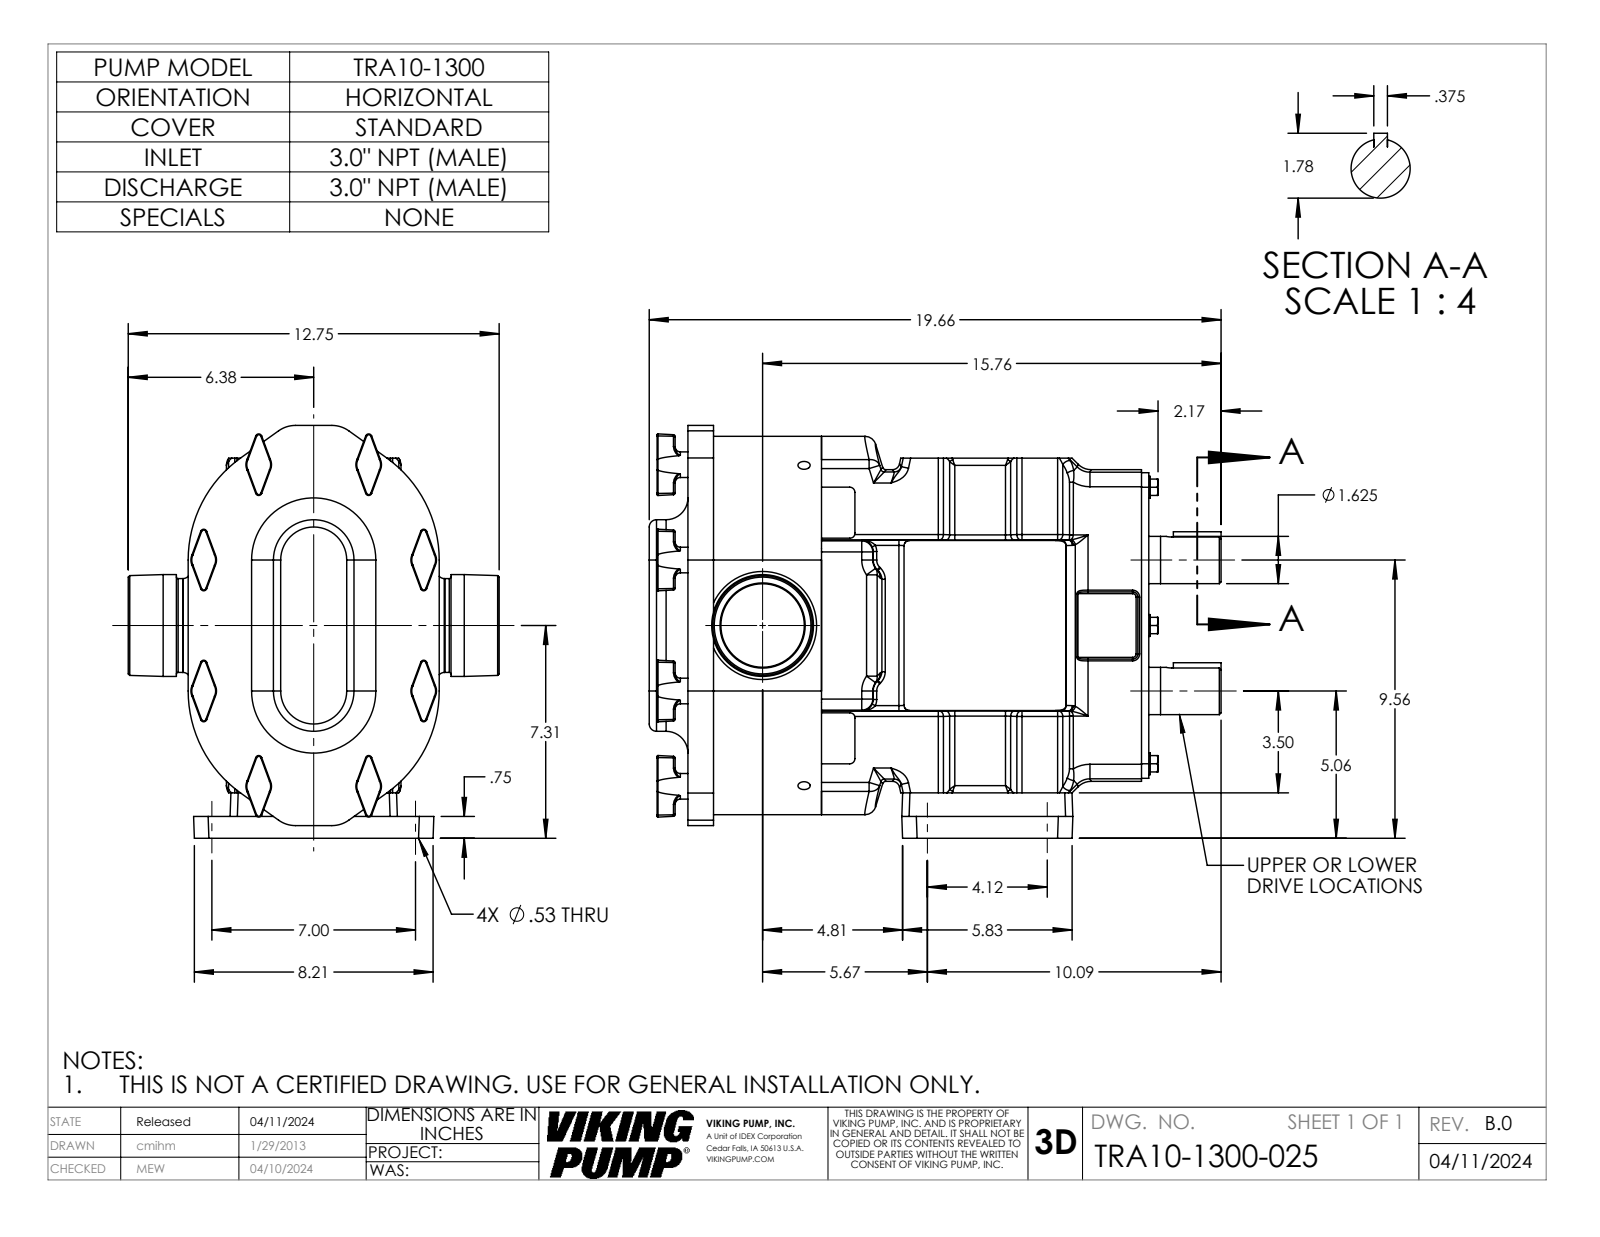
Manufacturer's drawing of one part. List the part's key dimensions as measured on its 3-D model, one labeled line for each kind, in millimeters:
Part name (STEP PRODUCT): TRA10-1300-025; TRA10-0600-COVER-STD; 1300NPT30; TRA10-0600-GEARBOX-H (+1 more)
STEP written by: SolidWorks 2022 (AUTOMOTIVE_DESIGN)
Units: millimetres
Bodies: 5 solids, 1071 faces (287 planar, 380 cylindrical, 404 other)
Overall size (bounding box): 499.3 × 360.3 × 323.9
Volume: 21 010 000 mm³ · Surface area: 916 800 mm²
Round holes (diameter × count): ⌀8.4 ×4, ⌀13.5 ×4, ⌀72.8 ×1
Round bosses / shafts (diameter × count): ⌀22.4 ×8, ⌀19.1 ×6, ⌀41.2 ×2, ⌀88.9 ×1, ⌀81.9 ×1
Partial cylindrical surfaces — rounded edges, fillets, slot ends (radius × count): R4.6 ×44, R1.5 ×43, R0.8 ×32, R6.4 ×32, R9.7 ×28, R3 ×24, R12.7 ×20, R9.5 ×12
Main face-to-face distances: 94.3, 12.7, 22.4, 116.6, 9.1, 402.4, 380, 285.8, 165.1, 19.1
Hole centre spacings: 73.5, 104.6, 177.8, 206.3
